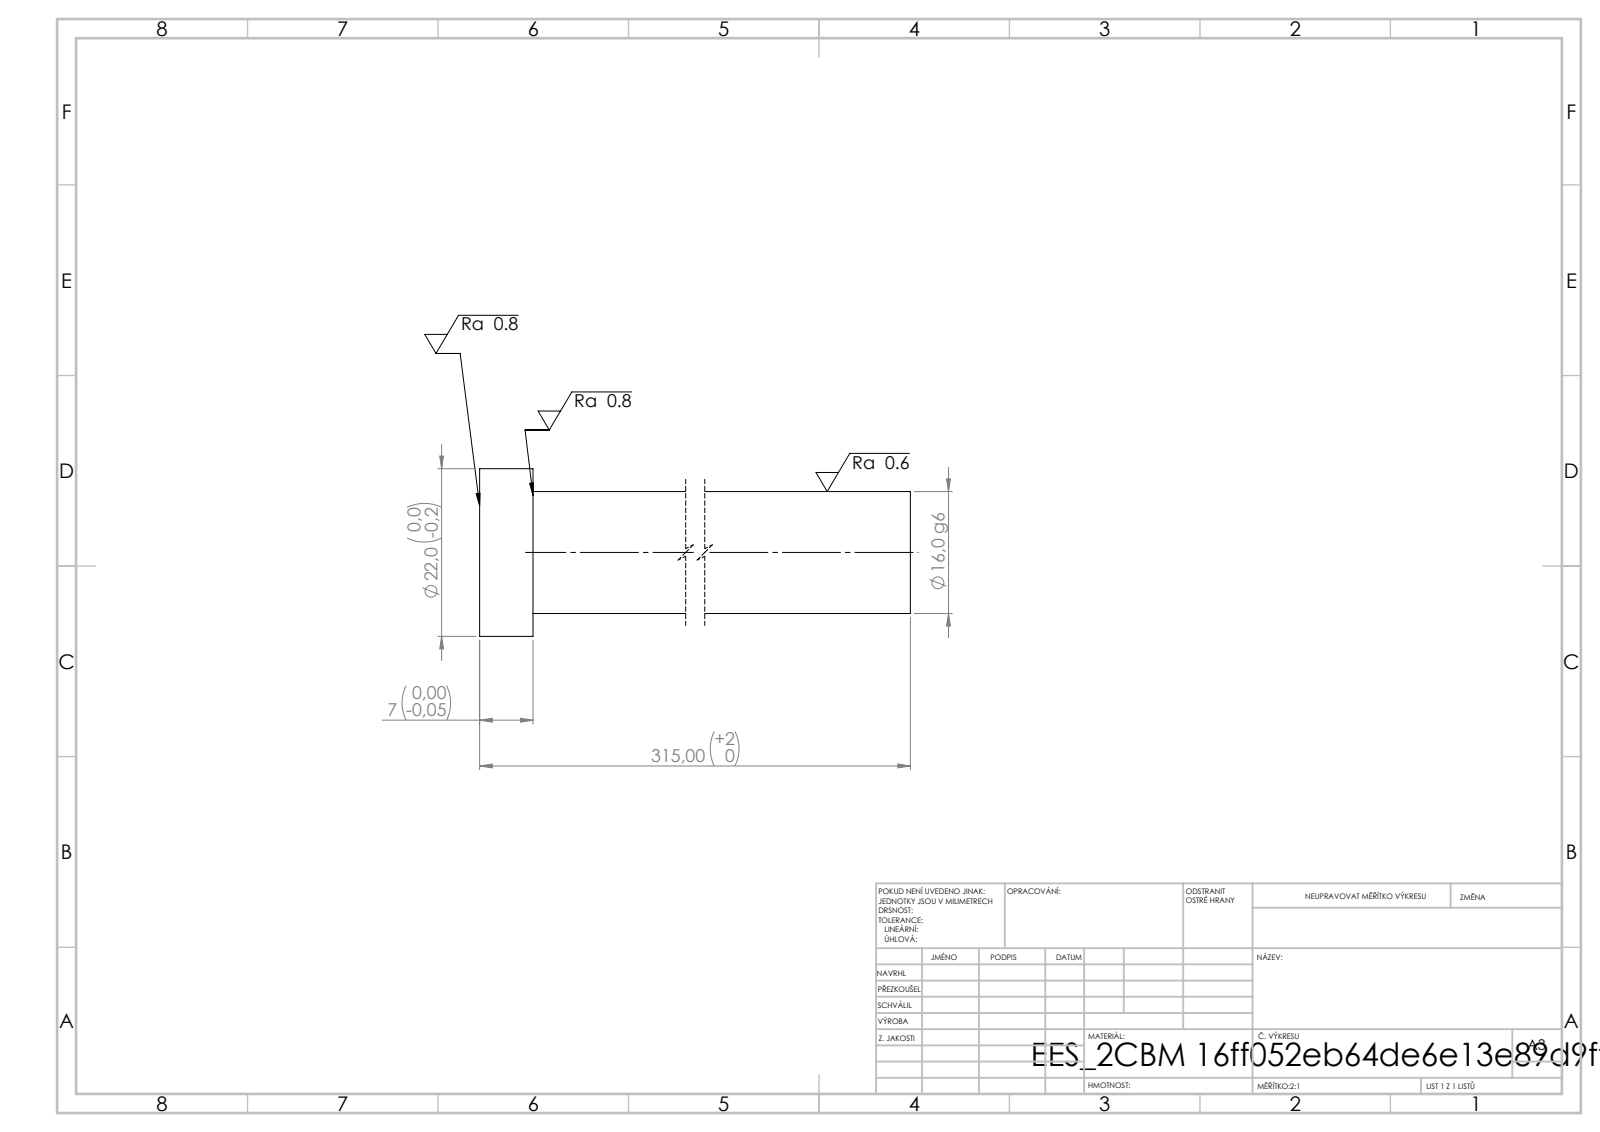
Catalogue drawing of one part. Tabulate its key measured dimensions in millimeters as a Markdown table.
| quantity | value |
| --- | --- |
| STEP written by | SolidWorks 2019 (CONFIG_CONTROL_DESIGN) |
| units | millimeters |
| bodies | 1 solid, 7 faces (3 planar, 4 cylindrical, 0 other) |
| overall size | 315 × 22 × 22 |
| volume | 64 588 mm³ |
| surface area | 16 726 mm² |
| round bosses / shafts (diameter × count) | 22 × 1, 16 × 1 |
| main face-to-face distances | 315, 7, 308 |
